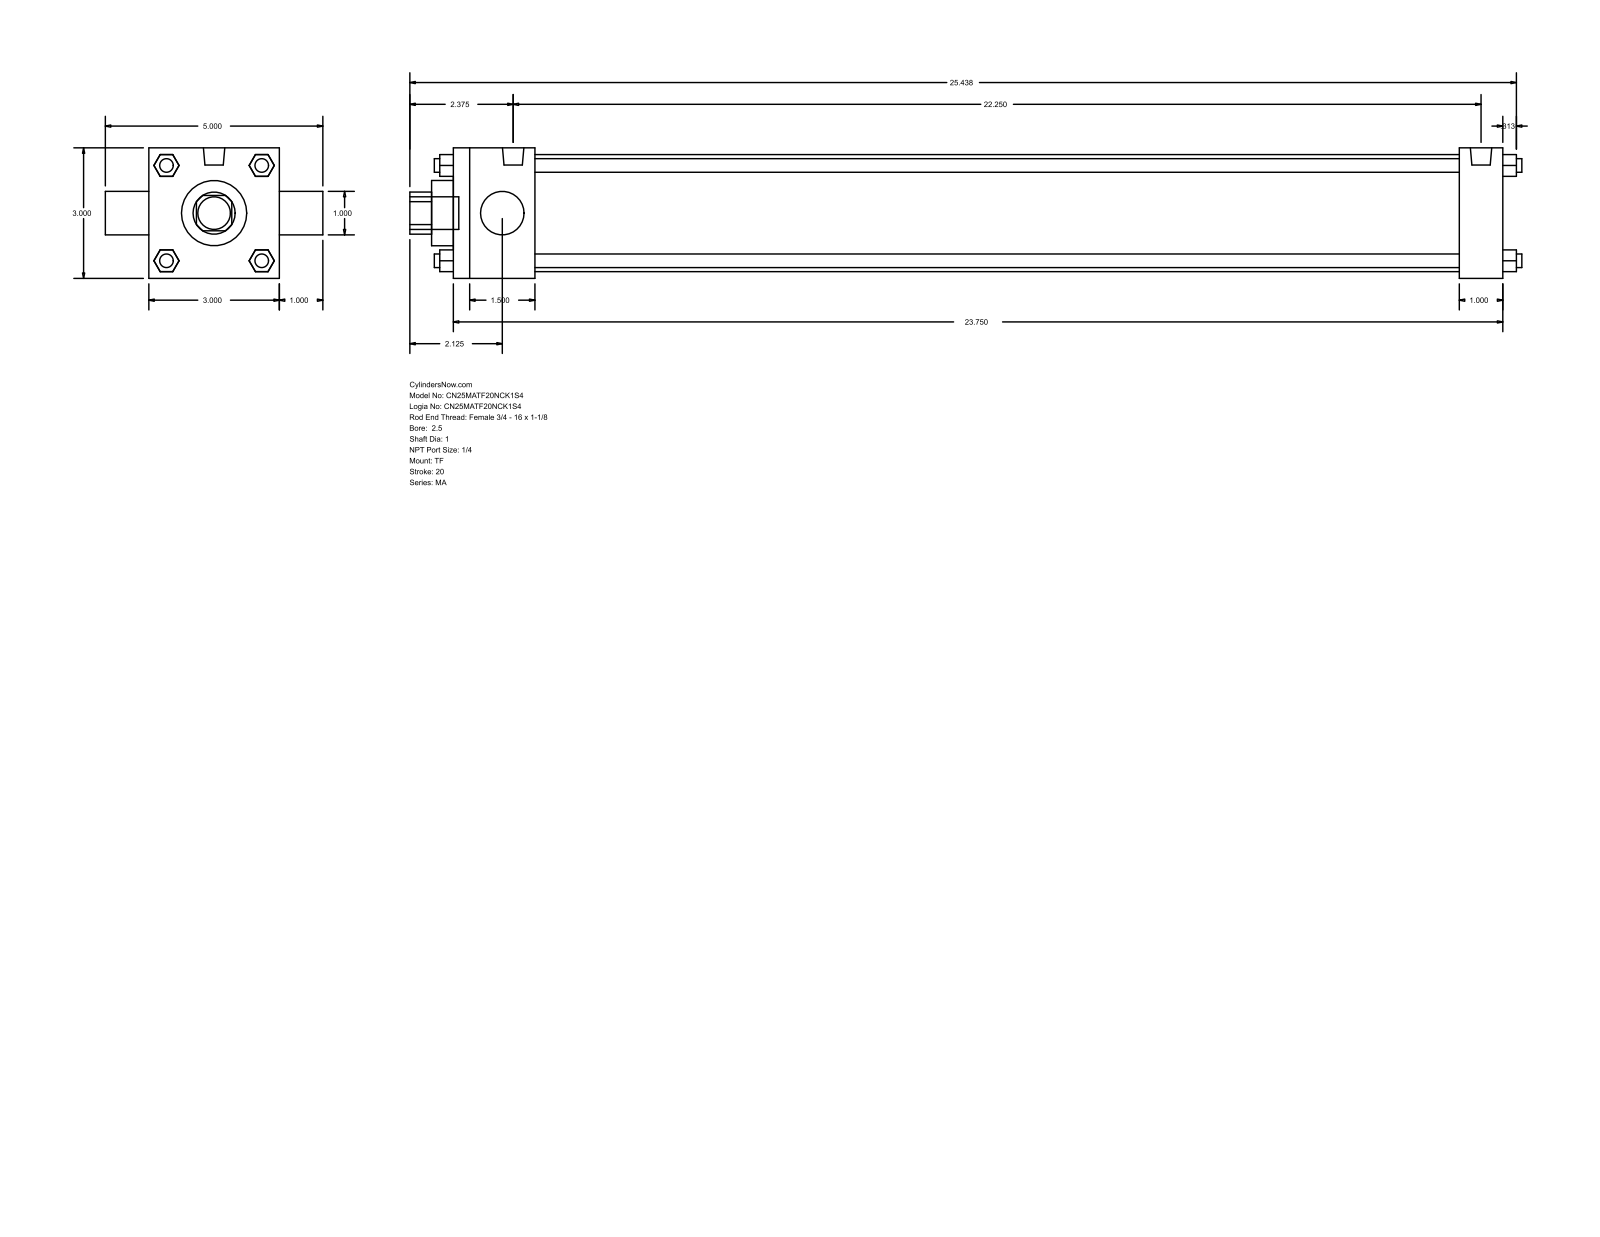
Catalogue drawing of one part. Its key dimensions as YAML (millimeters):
part_name: "MA_TF__0250_1"
step_written_by: "GSSL Pune (CONFIG_CONTROL_DESIGN)"
units: millimeters
bodies: {solids: 0, faces: 120, planar: 92, cylindrical: 28, other: 0}
overall_size: [649.29, 127, 76.2]
round_holes:
  - {diameter: 25.4, count: 2}
  - {diameter: 38.1, count: 1}
  - {diameter: 68.33, count: 1}
round_bosses_or_shafts:
  - {diameter: 7.94, count: 7}
  - {diameter: 12.49, count: 2}
  - {diameter: 19.05, count: 1}
partial_cylinders:
  - {radius: 12.29, count: 1}
face_to_face_distances: [76.2, 612.77, 25.4, 12.7, 47.63, 587.37, 539.74, 565.14, 101.6, 27.81]
